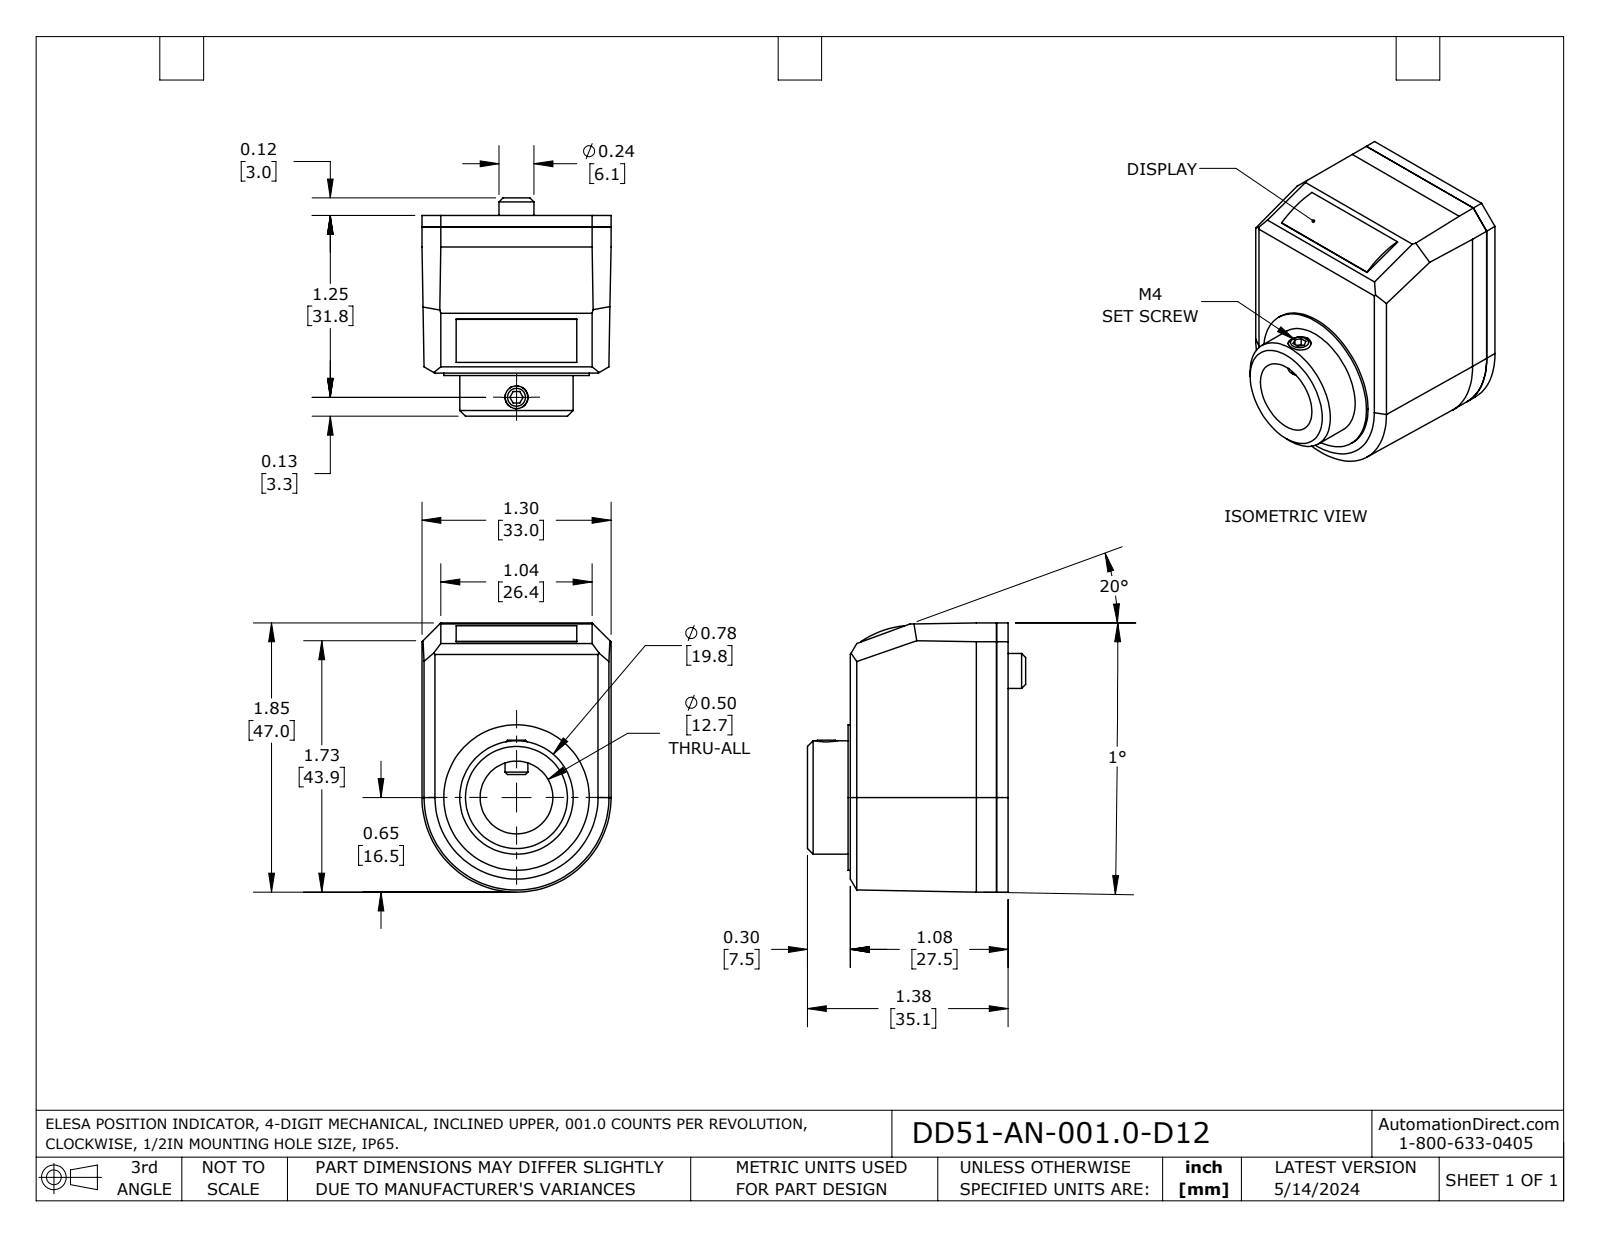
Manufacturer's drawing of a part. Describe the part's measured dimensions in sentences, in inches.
The part is named "DD51-AN-INCH". Its 3-D file was written by "SolidWorks 2023 (AUTOMOTIVE_DESIGN)". It is 4 solids with 77 faces: 59 planar, 12 cylindrical and 6 other. Overall it measures 1.85 by 1.5 by 1.3 inches. Its volume is 2.036 cubic inches and its surface area 20.14 square inches. Round holes: 1 of diameter 0.157, 1 of diameter 0.5, 1 of diameter 0.78, 1 of diameter 1.08. Round bosses or shafts: 1 of diameter 1, 1 of diameter 0.24, 1 of diameter 0.157. Partial cylindrical surfaces (rounded edges, fillets, slot ends): 1 of radius 0.65, 1 of radius 0.662. The main face-to-face distances are 0.08, 1.004, 1.084, 0.864, 0.14, 0.22, 1.3, 0.016, 0.88, 1.02.
